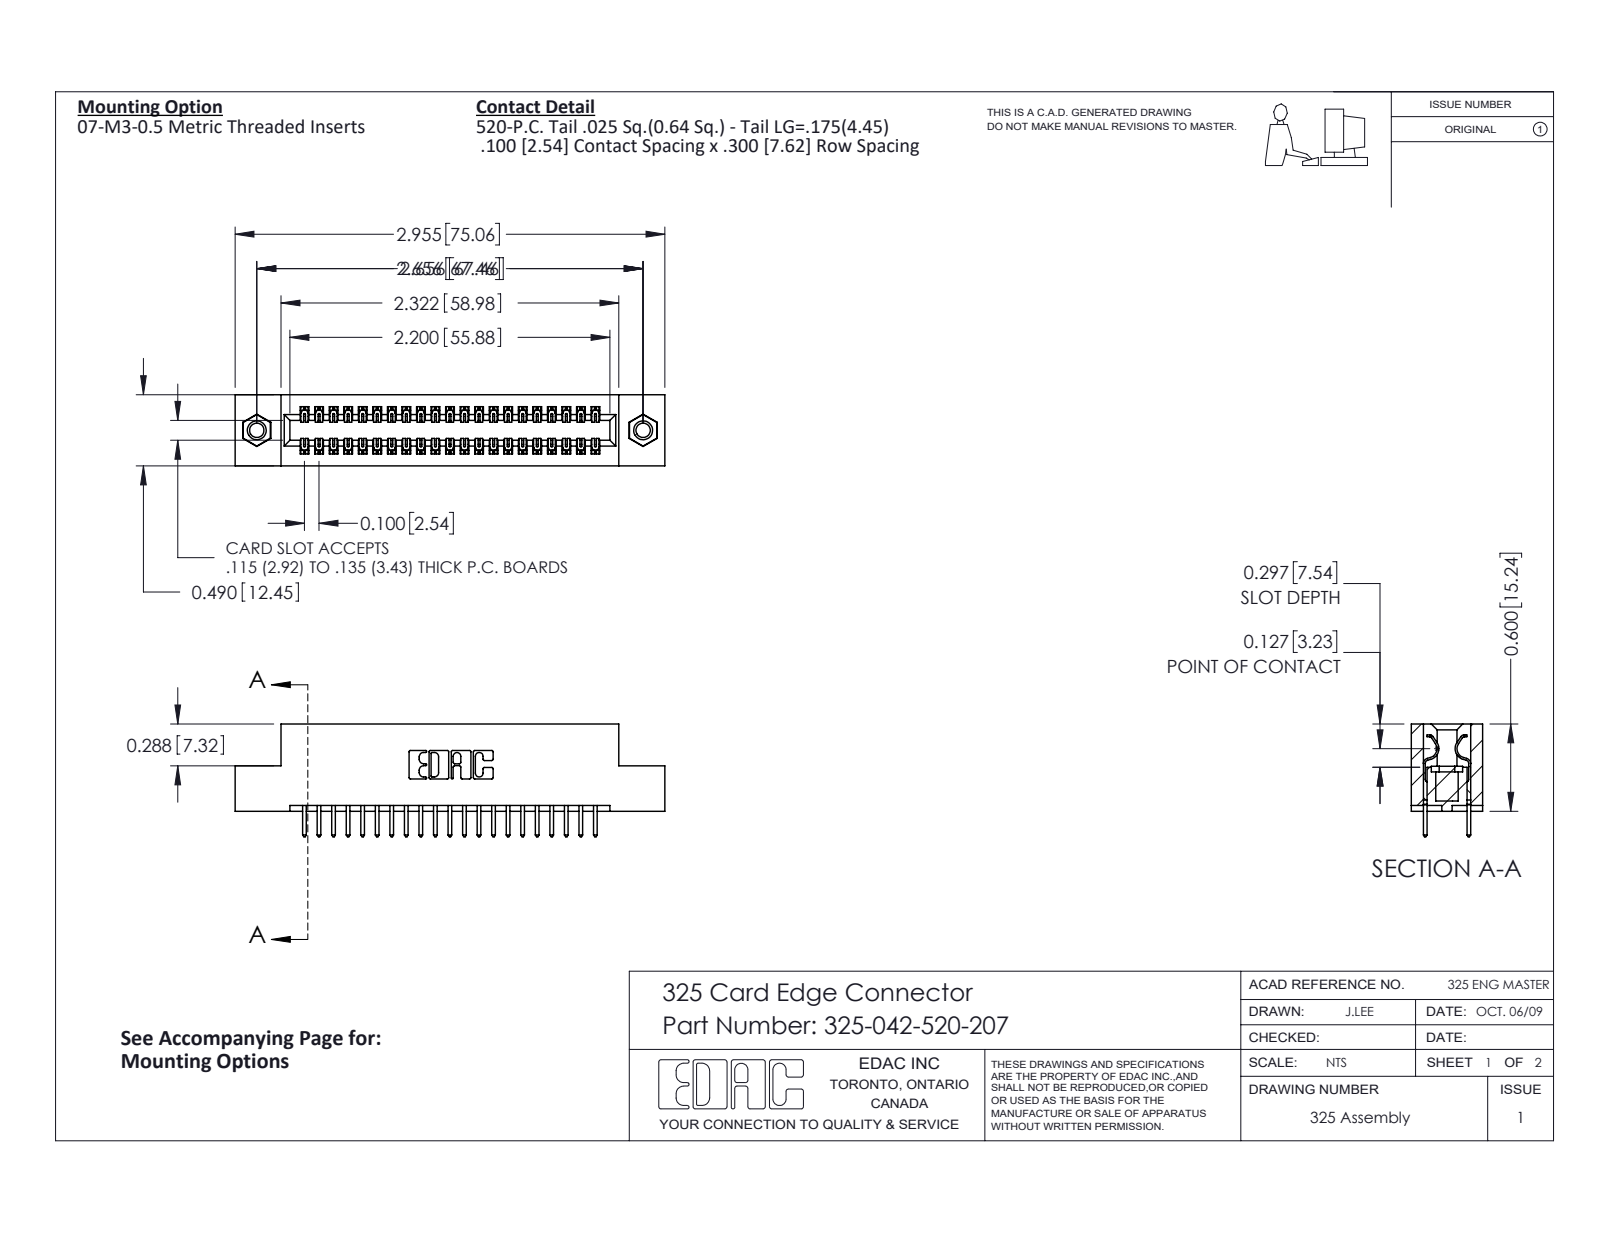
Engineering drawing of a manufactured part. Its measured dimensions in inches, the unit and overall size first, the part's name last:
Units: inches
Overall size (bounding box): 2.955 × 0.775 × 0.49
Round holes (diameter × count): ⌀0.098 ×2, ⌀0.125 ×2, ⌀0.16 ×2
Round bosses / shafts (diameter × count): ⌀0.155 ×2
Partial cylindrical surfaces — rounded edges, fillets, slot ends (radius × count): R0.006 ×63, R0.01 ×42, R0.01 ×22, R0.007 ×6, R0.031 ×6, R0.026 ×3, R0.014 ×2, R0.022 ×2
Main face-to-face distances: 0.083, 0.407, 0.3, 0.49, 0.107, 0.383, 0.025, 0.325, 0.6, 0.04
Hole centre spacings: 2.656
Volume: 0.579 in³ · Surface area: 16.92 in²
Bodies: 45 solids, 2358 faces (1614 planar, 728 cylindrical, 16 other)
Part name (STEP PRODUCT): 325 Part_TI; 325-292-001_325-293-120; 345-250-001_345-250-005-103; 325-042-520-207
STEP written by: SolidWorks 2016 (CONFIG_CONTROL_DESIGN)
